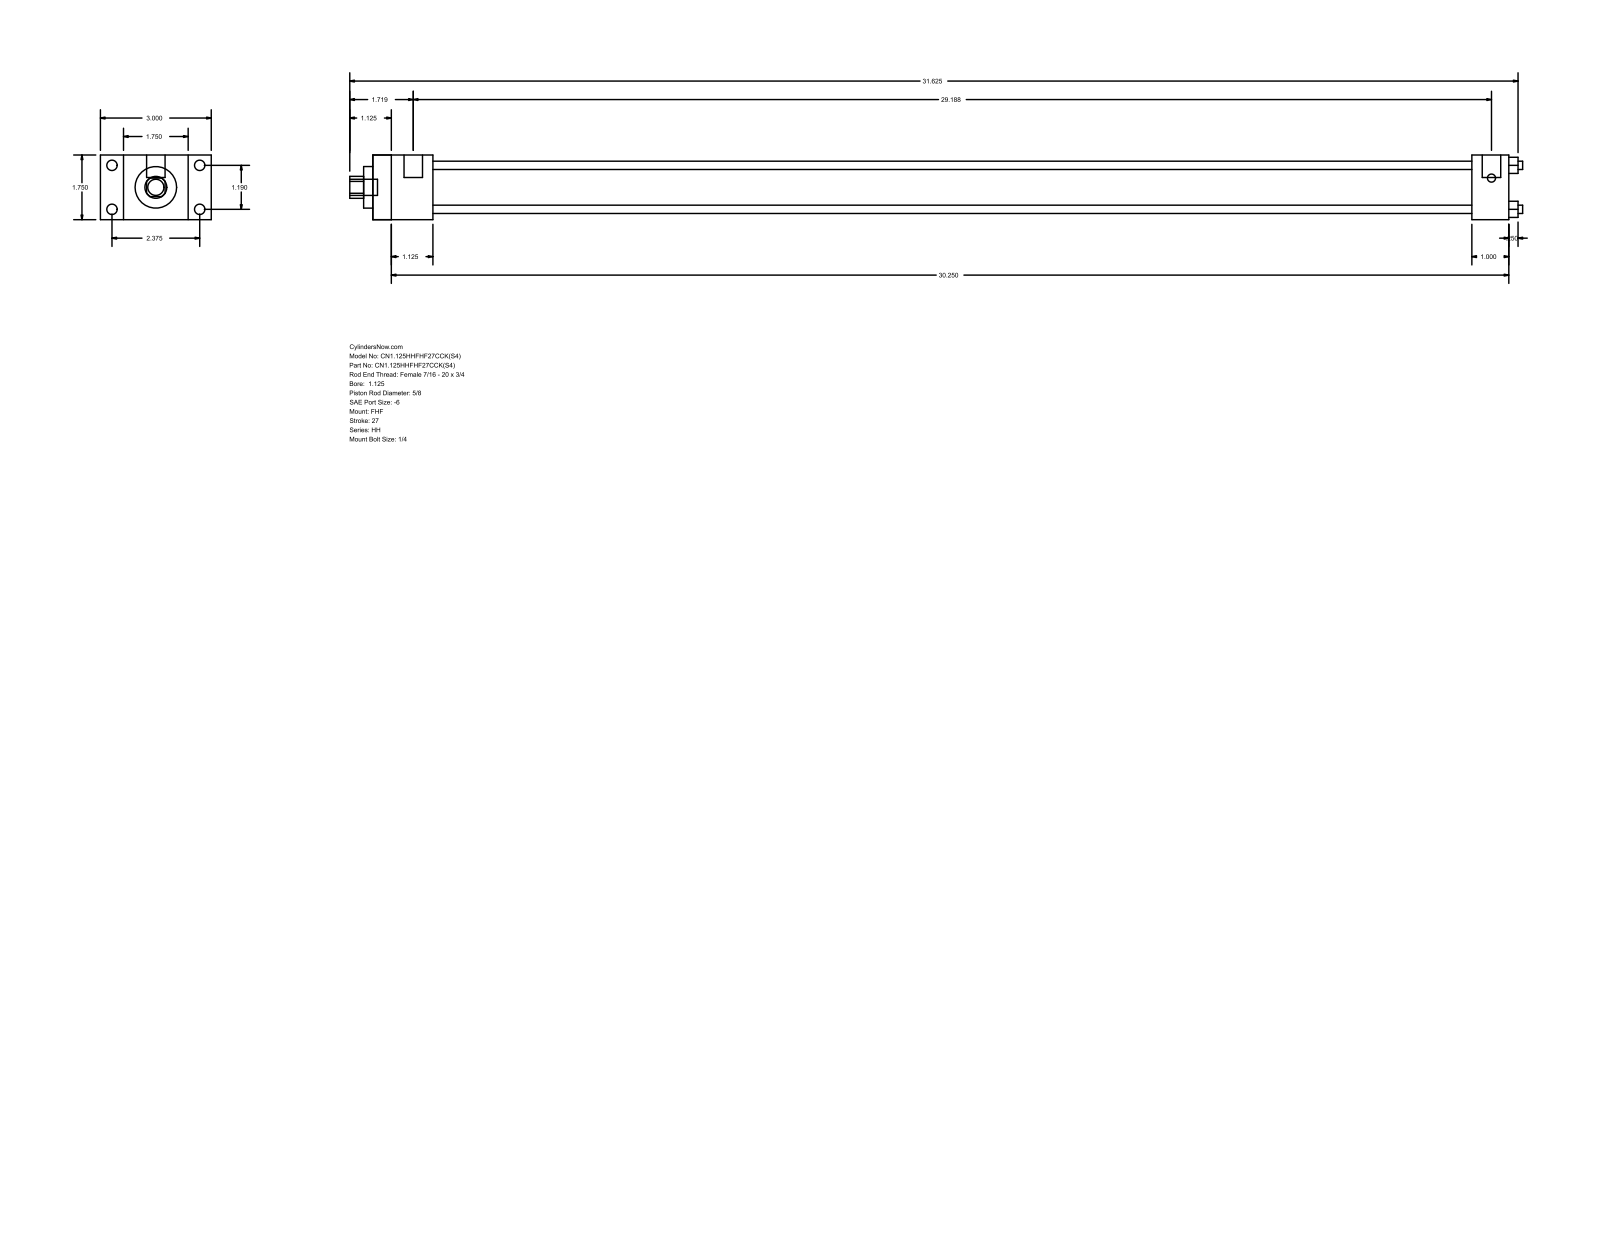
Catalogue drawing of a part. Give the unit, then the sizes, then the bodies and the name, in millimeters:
Units: millimetres
Overall size (bounding box): 806.45 × 76.2 × 44.45
Round holes (diameter × count): ⌀5.71 ×4, ⌀15.88 ×1, ⌀28.57 ×1, ⌀34.92 ×1
Round bosses / shafts (diameter × count): ⌀7.14 ×4, ⌀5.56 ×4, ⌀12.7 ×2, ⌀11.11 ×1
Partial cylindrical surfaces — rounded edges, fillets, slot ends (radius × count): R7.54 ×1
Main face-to-face distances: 44.46, 15.87, 60.33, 41.27, 76.2, 781.04, 739.77, 755.64, 714.37, 25.4
Hole centre spacings: 21.37, 30.22, 42.74
Bodies: 0 solids, 88 faces (60 planar, 28 cylindrical, 0 other)
Part name (STEP PRODUCT): HH_FHF__0112_0.625
STEP written by: GSSL Pune (CONFIG_CONTROL_DESIGN)
